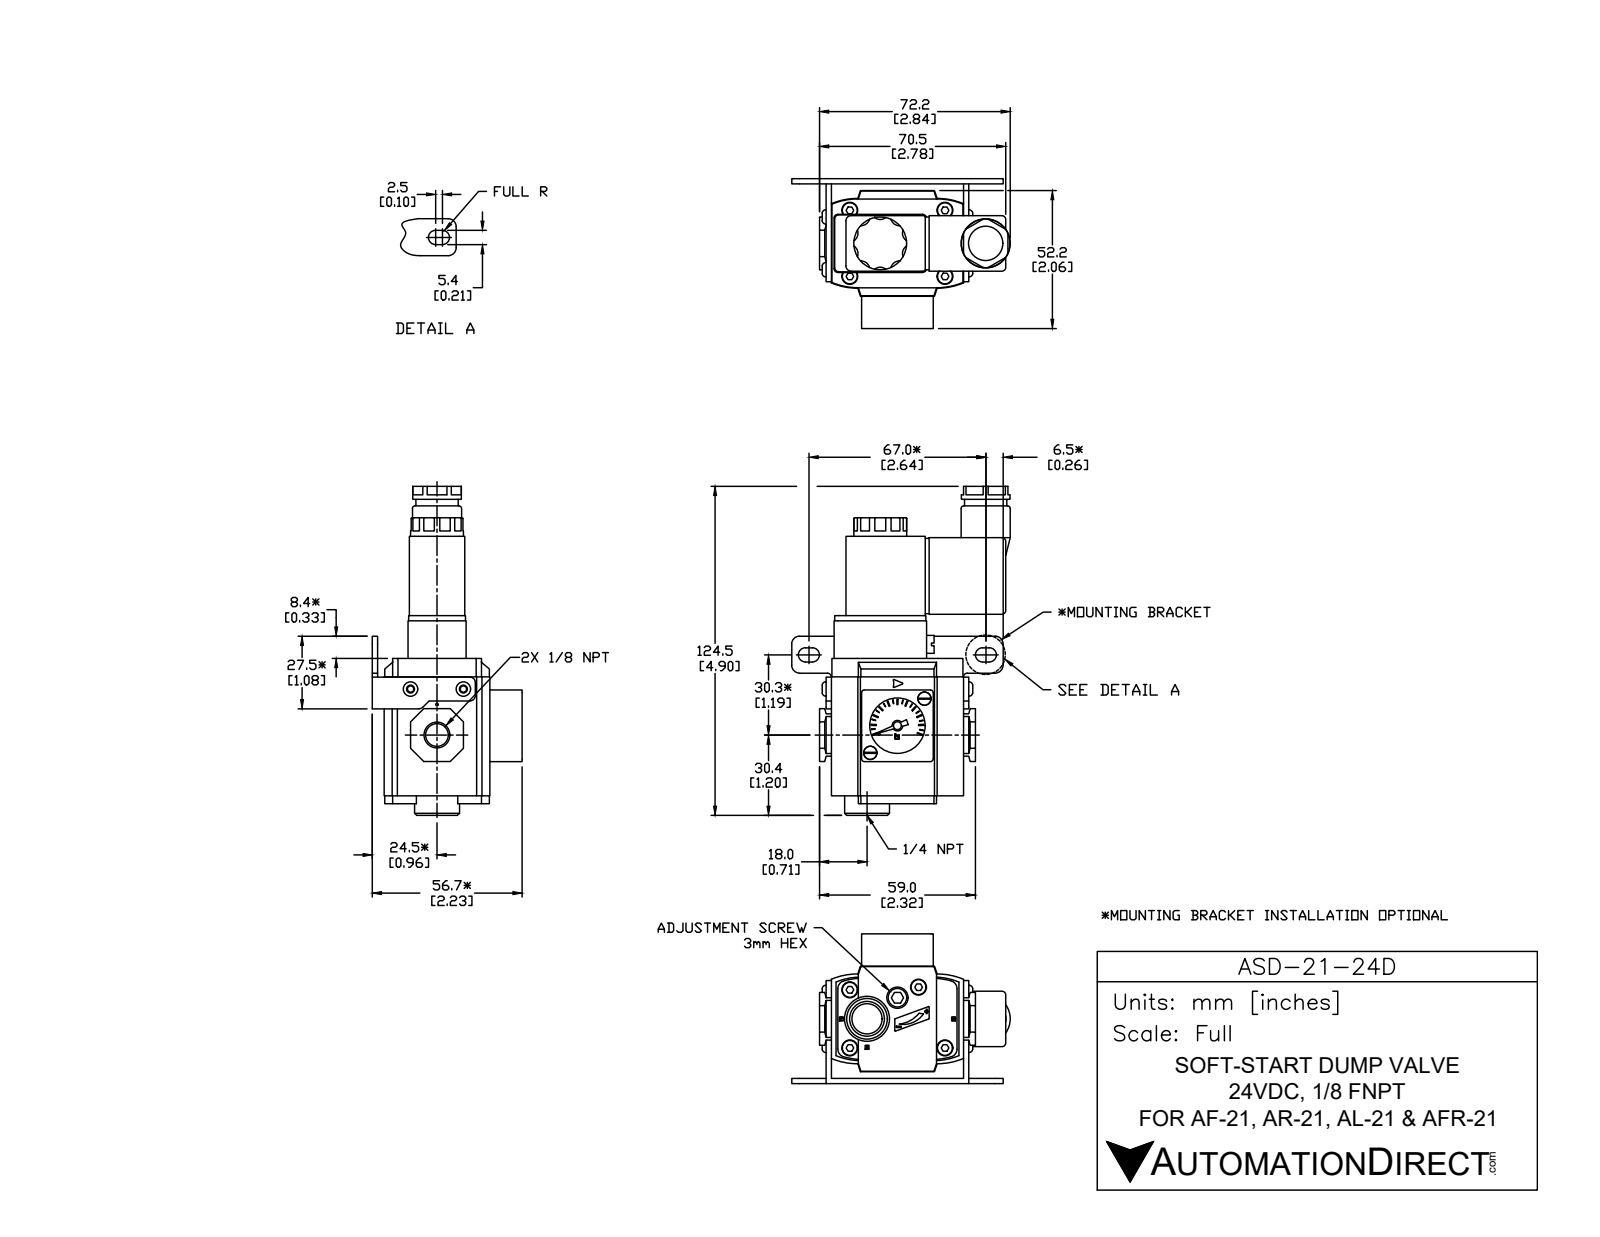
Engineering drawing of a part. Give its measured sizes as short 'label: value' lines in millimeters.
name: ASD-21-24D
written by: SolidWorks 2015 (CONFIG_CONTROL_DESIGN)
unit: mm
bodies: 22 solids, 568 faces (363 planar, 168 cylindrical, 37 other)
size: 124.5 × 82.7 × 56.7
volume: 166 361 mm³; area: 46 436 mm²
holes: 10× ⌀3, 8× ⌀6, 1× ⌀7, 1× ⌀8, 1× ⌀8.43, 1× ⌀11.45, 1× ⌀13, 1× ⌀17, 1× ⌀21
bosses: 4× ⌀5.6, 4× ⌀5.5, 2× ⌀2.5, 1× ⌀20, 1× ⌀18.6, 1× ⌀18.4, 1× ⌀16, 1× ⌀4
rounds: 10× R1.5, 10× R3.16, 6× R1, 6× R3, 4× R0.73, 4× R1.25, 4× R2.7, 4× R24.8
face distances: 52, 3, 2, 27.5, 6.5, 7, 45, 14, 5.5, 2.5
hole spacings: 1.5, 23.5, 36, 36.03, 42.99, 12.78, 14.09, 14.5
